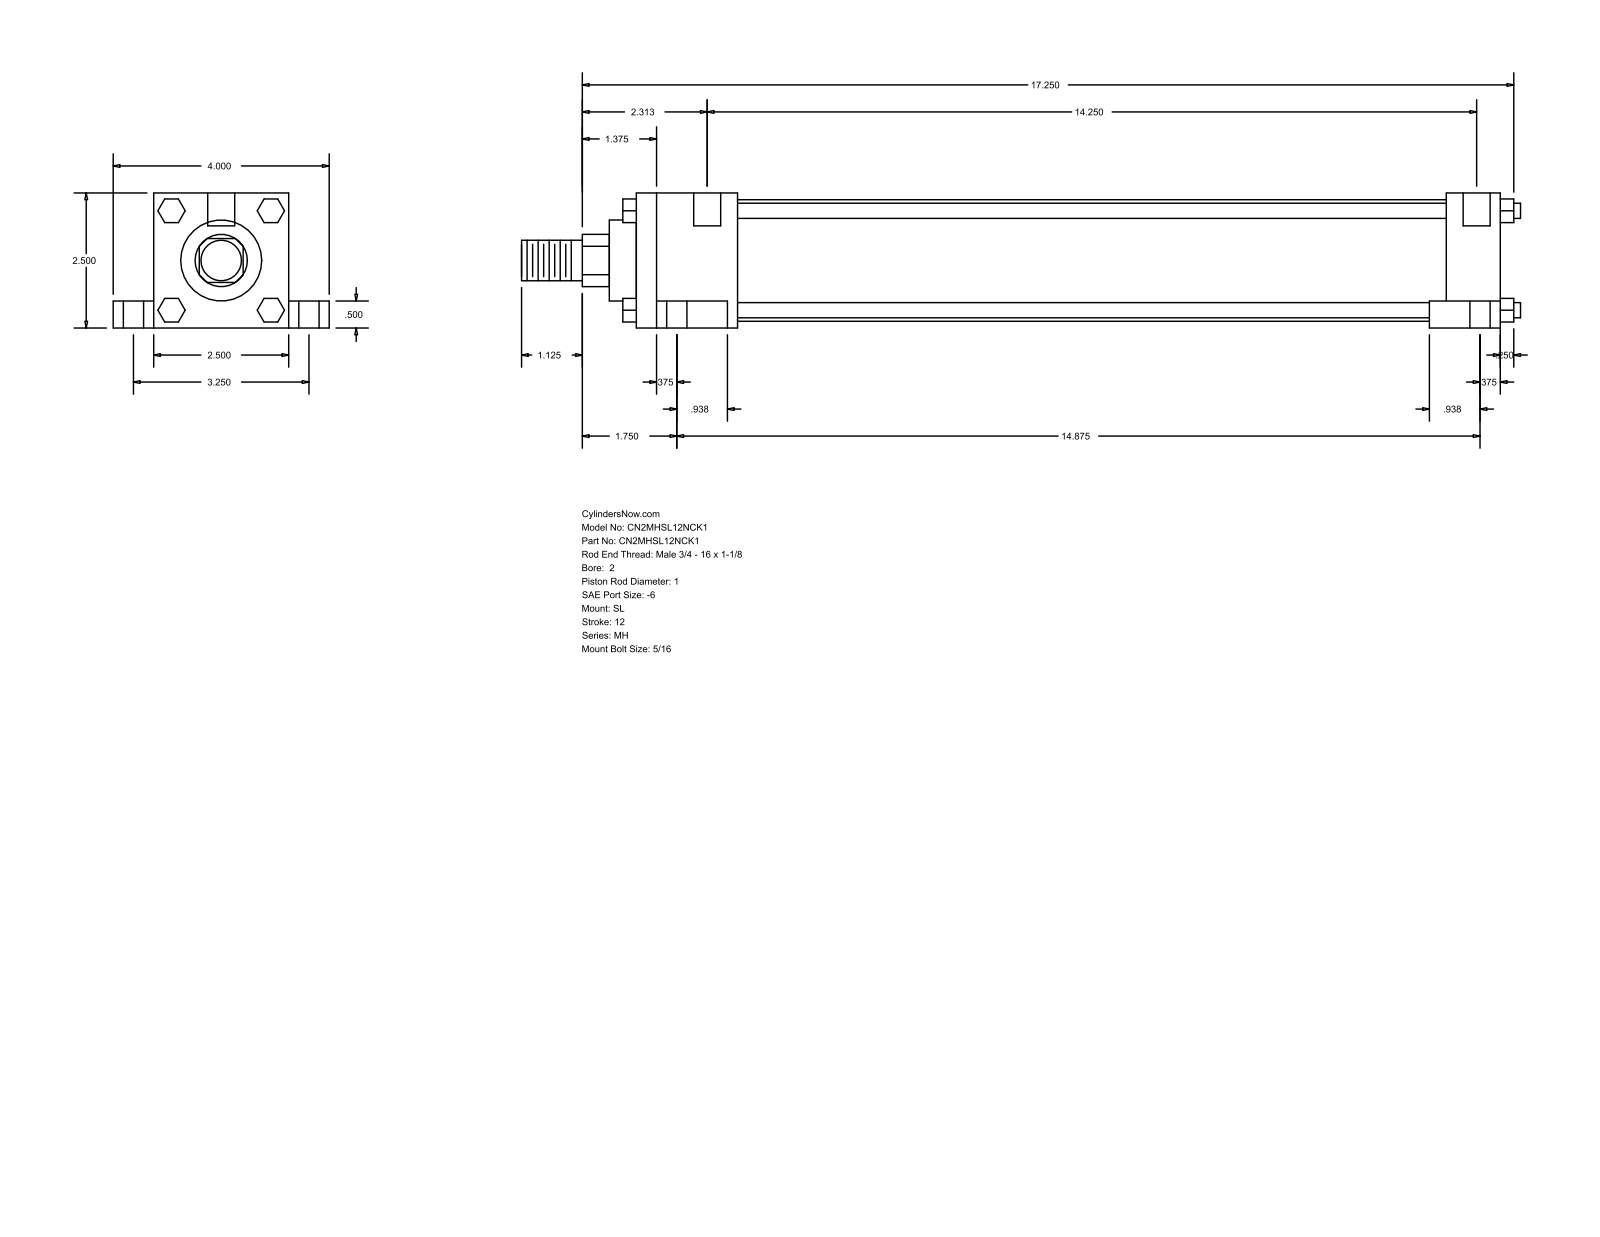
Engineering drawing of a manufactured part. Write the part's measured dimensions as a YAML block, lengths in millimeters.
part_name: "MH_SL__0200_1"
step_written_by: "GSSL Pune (CONFIG_CONTROL_DESIGN)"
units: millimeters
bodies: {solids: 0, faces: 148, planar: 112, cylindrical: 36, other: 0}
overall_size: [469.9, 101.6, 63.5]
round_holes:
  - {diameter: 5.56, count: 4}
  - {diameter: 9.53, count: 4}
  - {diameter: 15.88, count: 4}
  - {diameter: 12.7, count: 2}
round_bosses_or_shafts:
  - {diameter: 7.14, count: 4}
  - {diameter: 57.15, count: 1}
  - {diameter: 38.1, count: 1}
  - {diameter: 25.4, count: 1}
  - {diameter: 19.05, count: 1}
partial_cylinders:
  - {radius: 12.29, count: 1}
face_to_face_distances: [63.5, 406.4, 12.7, 19.05, 50.8, 82.55, 25.4, 381, 47.63, 333.37]
hole_center_spacings: [41.3, 42.36, 43.67, 82.54, 365.87, 369.88, 370.6, 377.82]
